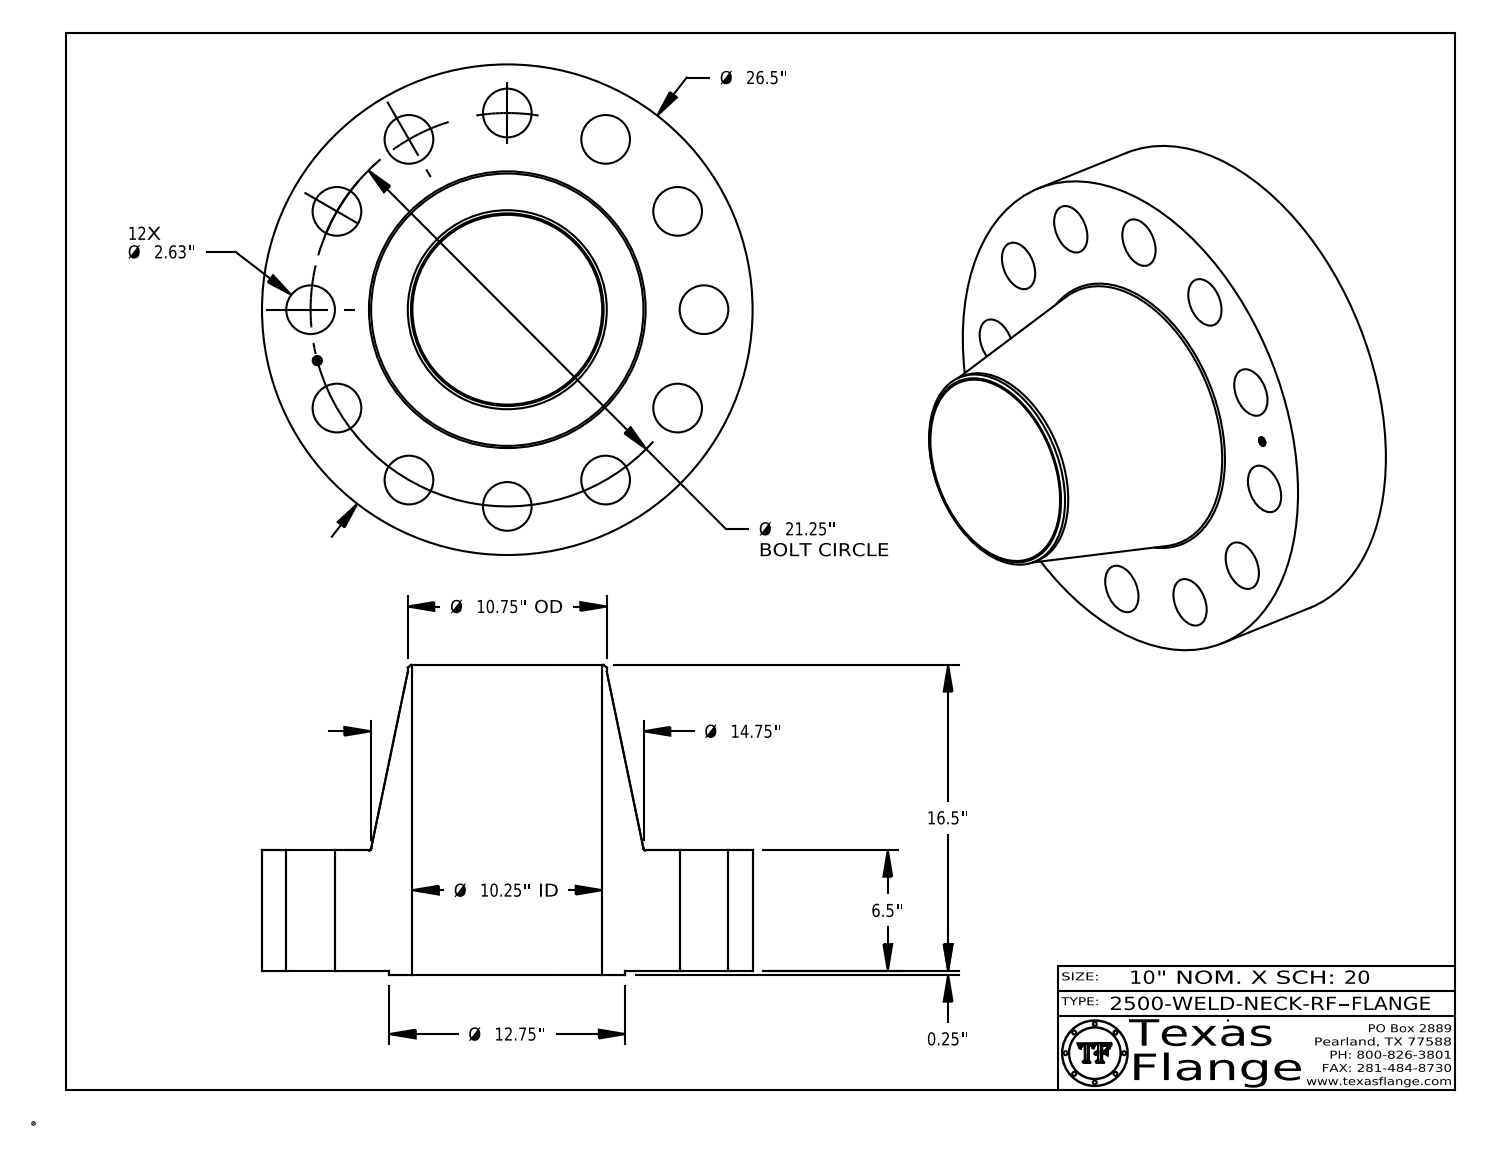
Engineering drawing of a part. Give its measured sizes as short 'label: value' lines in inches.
name: 2500-WELD-NECK-RF
written by: CATIA V5 STEP AP214 (AUTOMOTIVE_DESIGN)
unit: in
bodies: 1 solid, 427 faces (369 planar, 52 cylindrical, 6 other)
size: 26.5 × 26.5 × 16.75
volume: 3 084 in³; area: 2 865 in²
holes: 12× ⌀2.63, 1× ⌀0.495, 1× ⌀10.25
bosses: 8× ⌀0.03, 1× ⌀26.5, 1× ⌀12.75, 1× ⌀10.75, 1× ⌀0.39
face distances: 6.5, 0.25, 6.75, 16.75, 16.5, 10, 6.735, 6.485, 0.015, 10.015
hole spacings: 10.625, 5.5, 18.403, 15.026, 20.526, 15.026, 20.526, 21.25
